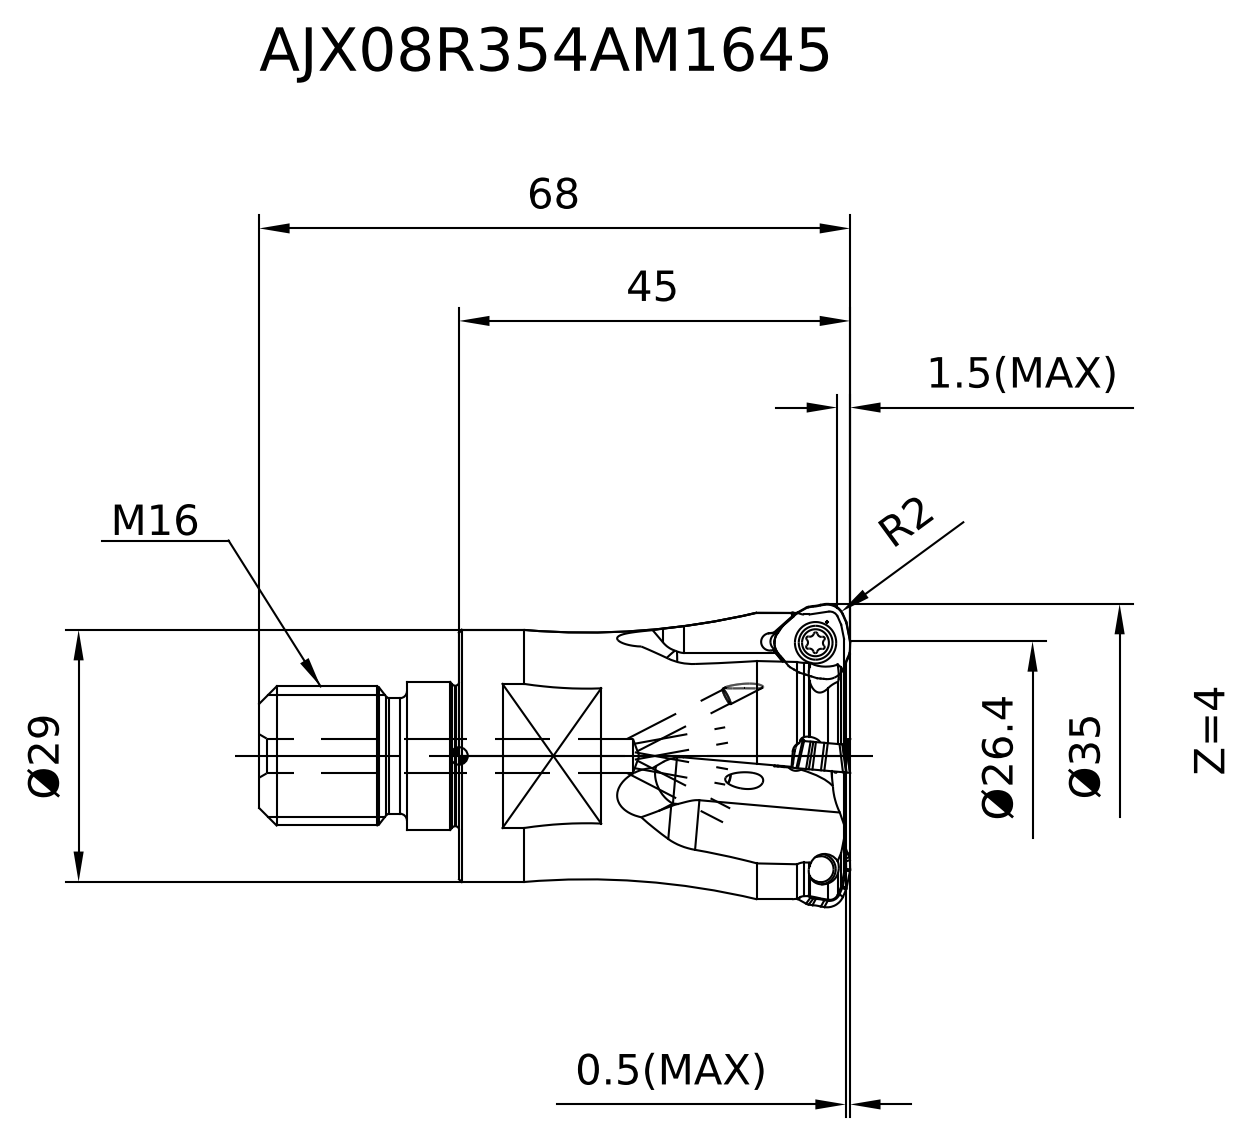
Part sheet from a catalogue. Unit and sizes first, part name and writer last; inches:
Units: inches
Overall size (bounding box): 2.677 × 1.304 × 1.304
Round holes (diameter × count): ⌀0.071 ×4, ⌀0.079 ×4, ⌀0.118 ×4, ⌀0.138 ×4, ⌀0.063 ×1, ⌀0.157 ×1
Round bosses / shafts (diameter × count): ⌀0.154 ×4, ⌀0.112 ×4, ⌀1.142 ×1, ⌀0.669 ×1, ⌀0.638 ×1, ⌀0.63 ×1, ⌀0.524 ×1
Partial cylindrical surfaces — rounded edges, fillets, slot ends (radius × count): R0.009 ×24, R0.019 ×24, R0.039 ×24, R0.03 ×16, R0.043 ×12, R0.008 ×8, R0.118 ×8, R0.161 ×4
Main face-to-face distances: 0.937, 1.676, 2.581, 0.906, 0.121, 1.479, 0.197, 1.102, 0.068, 1.547
Volume: 1.758 in³ · Surface area: 13.65 in²
Bodies: 5 solids, 499 faces (102 planar, 206 cylindrical, 191 other)
Part name (STEP PRODUCT): AJX08R354AM1645_ASM
STEP written by: SIEMENS PLM Software NX 10.0 (AUTOMOTIVE_DESIGN)
